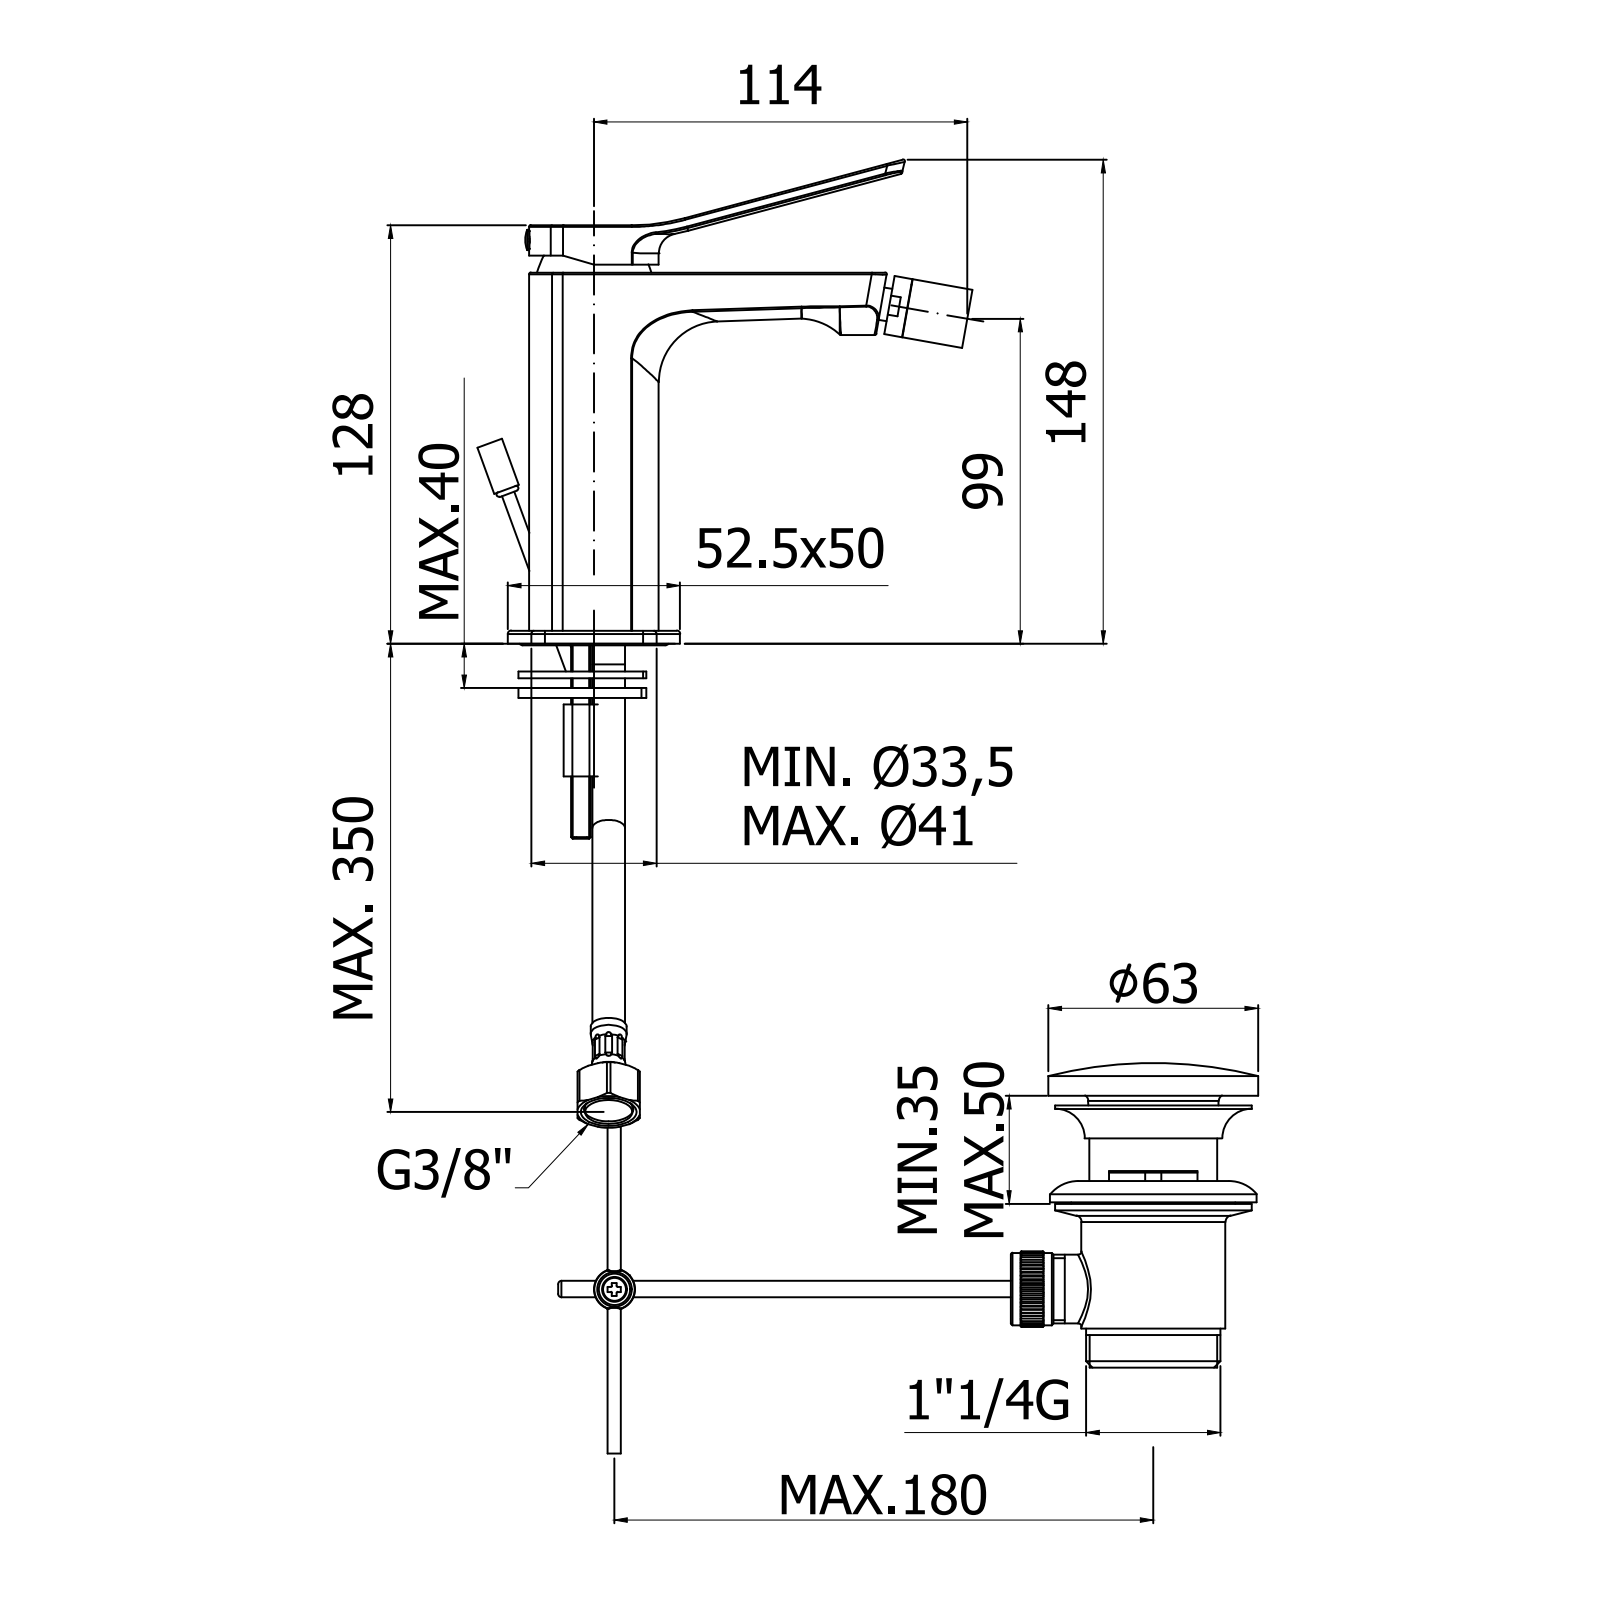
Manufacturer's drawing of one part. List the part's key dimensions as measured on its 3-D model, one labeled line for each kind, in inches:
Part name (STEP PRODUCT): TI135CR
STEP written by: CREO PARAMETRIC BY PTC INC, 2020044 (CONFIG_CONTROL_DESIGN)
Units: inches
Bodies: 3 solids, 551 faces (120 planar, 208 cylindrical, 223 other)
Overall size (bounding box): 5.95 × 5.813 × 1.969
Volume: 5.587 in³ · Surface area: 102.1 in²
Round holes (diameter × count): ⌀0.197 ×3, ⌀0.165 ×2, ⌀0.244 ×2, ⌀0.157 ×1, ⌀0.217 ×1, ⌀0.315 ×1, ⌀0.394 ×1, ⌀0.512 ×1, ⌀0.591 ×1, ⌀1.043 ×1, ⌀1.102 ×1, ⌀1.142 ×1
Round bosses / shafts (diameter × count): ⌀0.157 ×2, ⌀1.614 ×1, ⌀1.299 ×1, ⌀1.252 ×1, ⌀1.193 ×1, ⌀0.709 ×1, ⌀0.571 ×1, ⌀0.394 ×1
Partial cylindrical surfaces — rounded edges, fillets, slot ends (radius × count): R0.039 ×49, R0.02 ×20, R0.197 ×14, R0.177 ×4, R0.866 ×2, R0.965 ×2, R0.979 ×2, R1.578 ×2
Main face-to-face distances: 0.098, 4.358, 4.457, 0.669, 0.059, 0.157, 0.512, 4.811, 4.201, 4.299
Hole centre spacings: 0.461, 0.513, 0.433, 0.866
